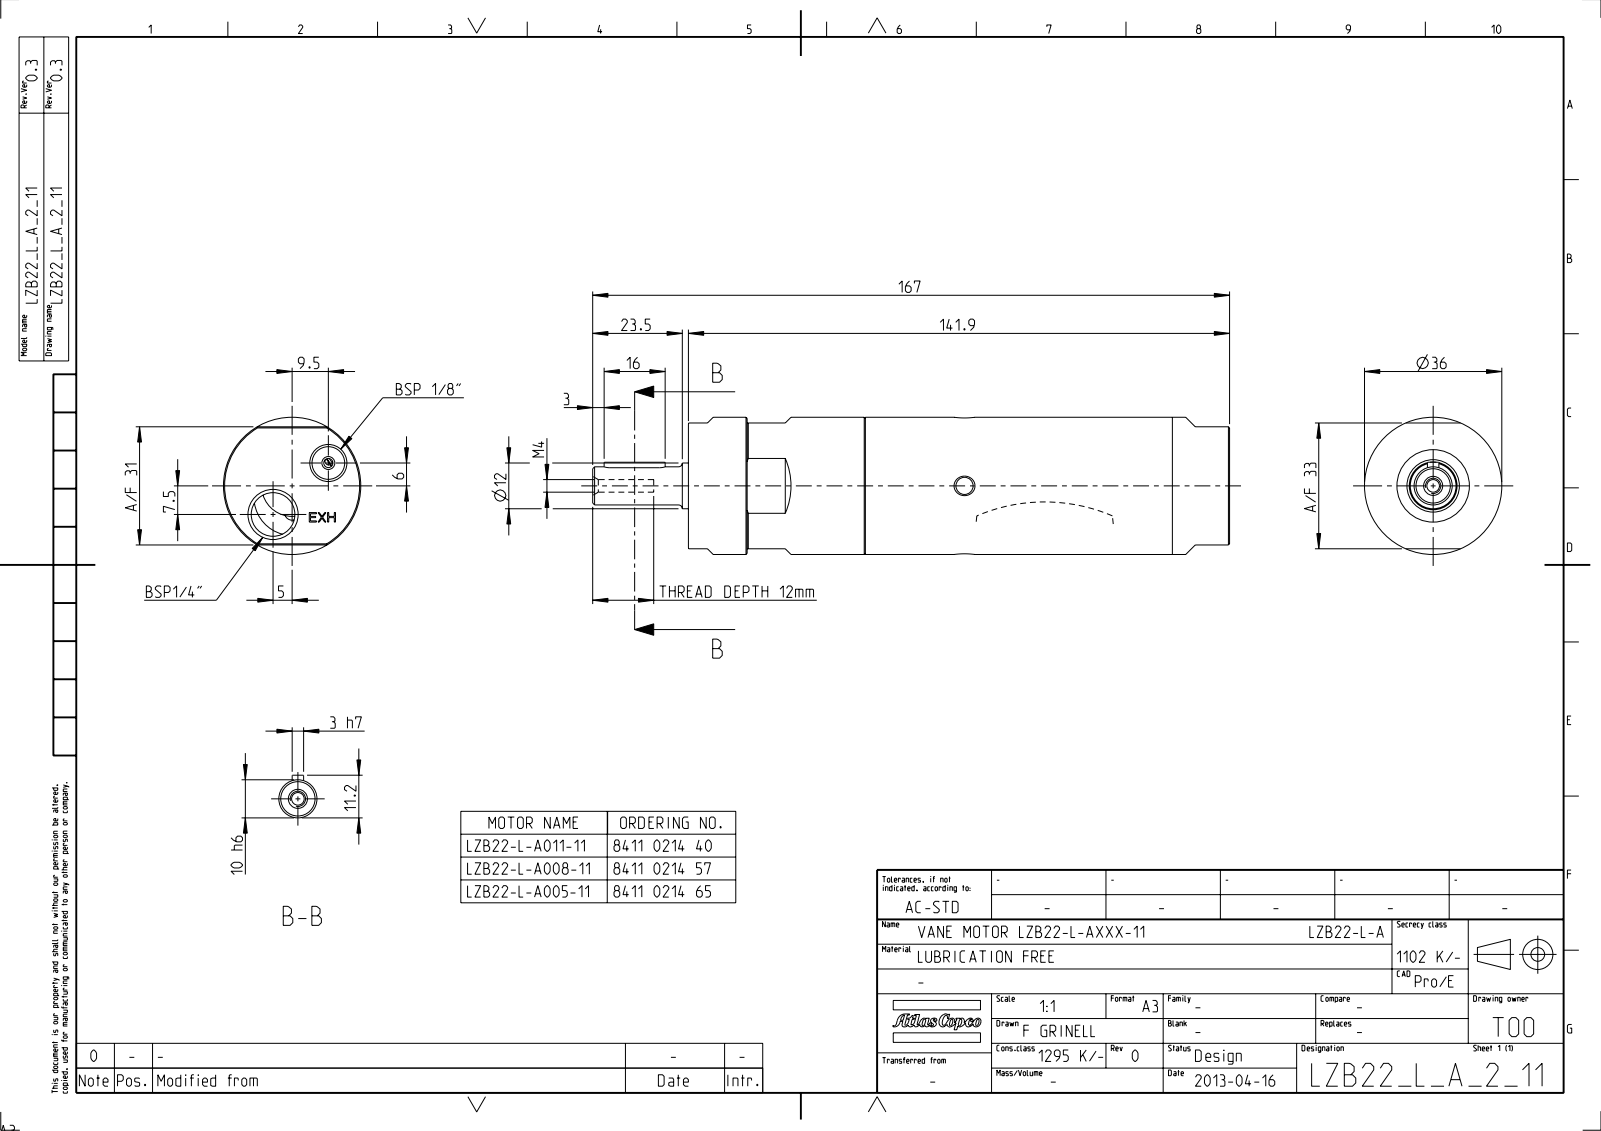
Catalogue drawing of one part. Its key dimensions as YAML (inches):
part_name: "4110106500; 4110106700; 4110106782_ASM; 4110107600 (+5 more)"
step_written_by: "CREO PARAMETRIC BY PTC INC, 2015080 (CONFIG_CONTROL_DESIGN)"
units: inches
bodies: {solids: 7, faces: 332, planar: 119, cylindrical: 119, other: 94}
overall_size: [6.575, 1.417, 1.417]
volume: 3.759
surface_area: 70.44
round_holes:
  - {diameter: 0.094, count: 2}
  - {diameter: 0.118, count: 2}
  - {diameter: 0.177, count: 2}
  - {diameter: 0.13, count: 1}
  - {diameter: 0.157, count: 1}
  - {diameter: 0.337, count: 1}
  - {diameter: 0.374, count: 1}
  - {diameter: 0.451, count: 1}
  - {diameter: 0.748, count: 1}
  - {diameter: 0.787, count: 1}
  - {diameter: 1.028, count: 1}
  - {diameter: 1.102, count: 1}
round_bosses_or_shafts:
  - {diameter: 1.417, count: 1}
  - {diameter: 1.25, count: 1}
  - {diameter: 1.181, count: 1}
  - {diameter: 0.984, count: 1}
  - {diameter: 0.886, count: 1}
  - {diameter: 0.518, count: 1}
  - {diameter: 0.472, count: 1}
  - {diameter: 0.394, count: 1}
partial_cylinders:
  - {radius: 0.004, count: 4}
  - {radius: 0.059, count: 2}
  - {radius: 0.06, count: 2}
  - {radius: 1.24, count: 2}
  - {radius: 0.098, count: 1}
  - {radius: 0.197, count: 1}
  - {radius: 0.295, count: 1}
  - {radius: 0.335, count: 1}
face_to_face_distances: [0.591, 5.587, 0.128, 0.404, 1.22, 4.996, 0.453, 4.98, 4.39, 0.606]
hole_center_spacings: [0.346, 0.692, 0.118, 0.165, 0.203, 0.228, 0.265, 0.355]
